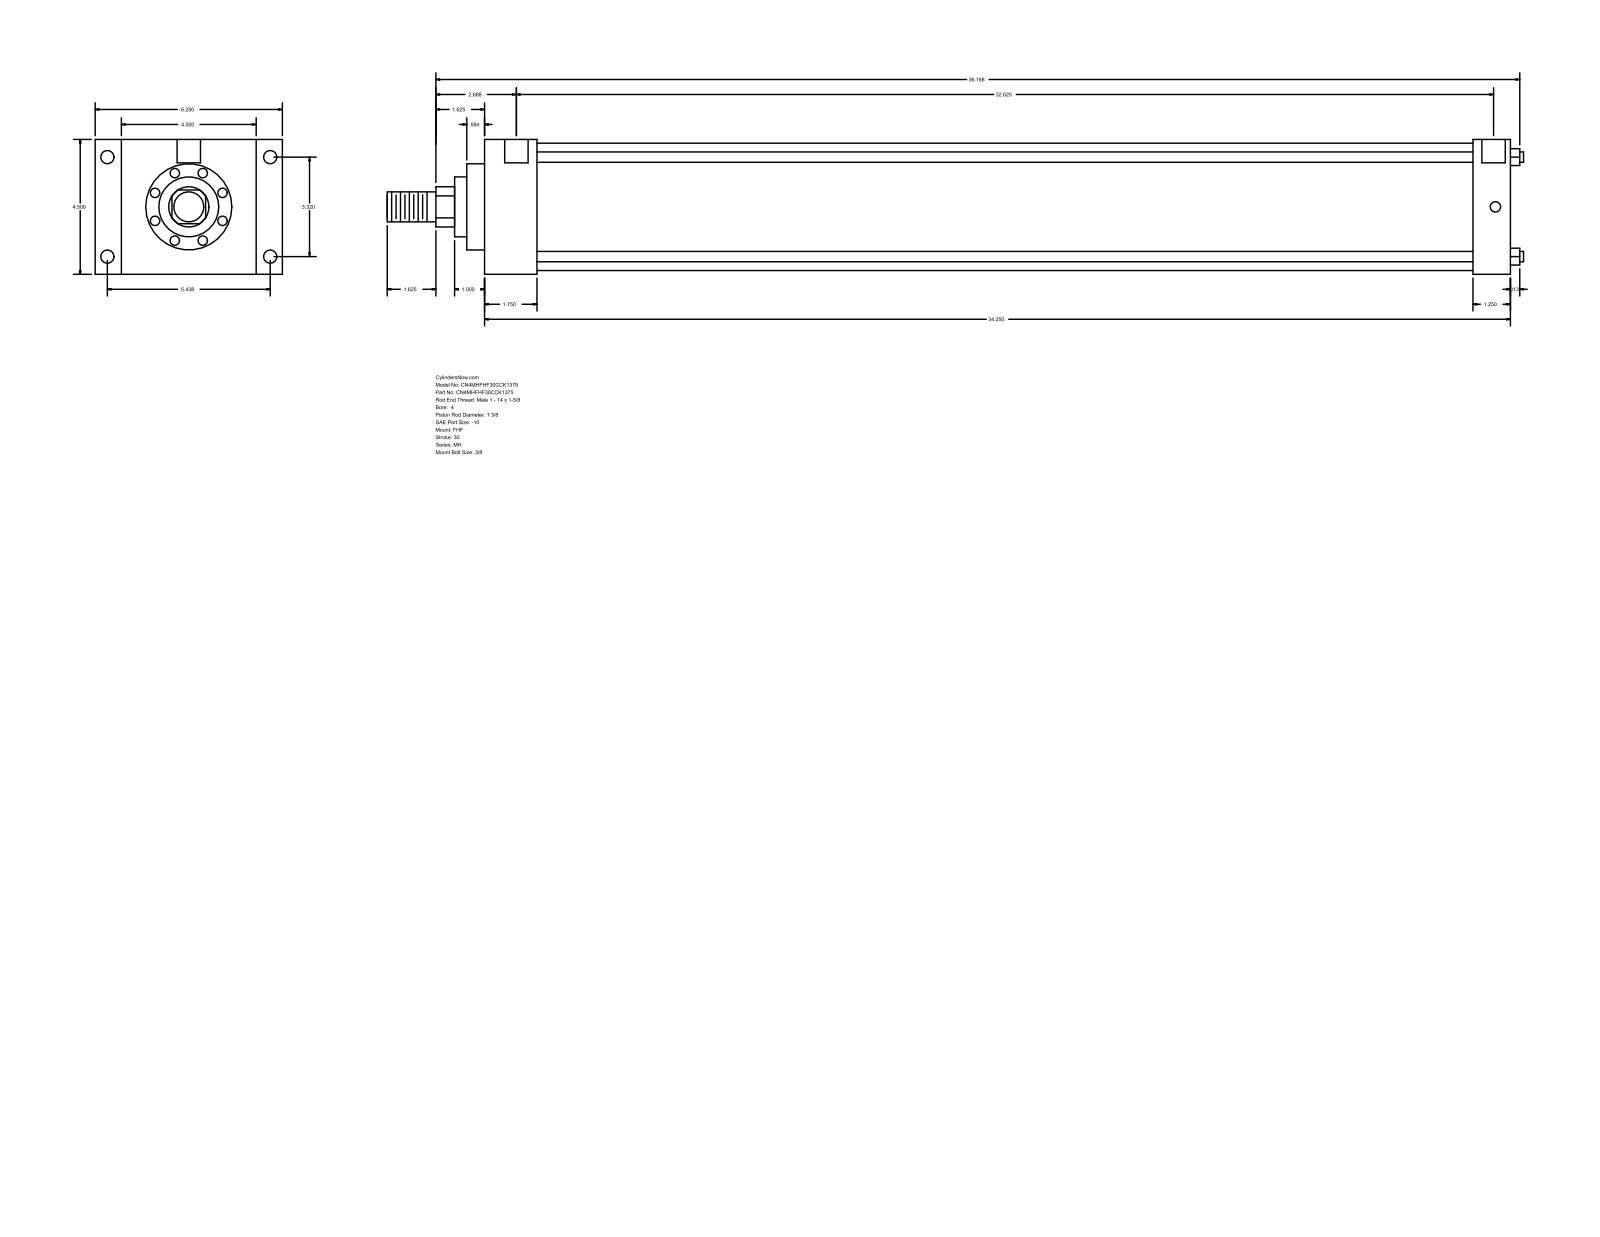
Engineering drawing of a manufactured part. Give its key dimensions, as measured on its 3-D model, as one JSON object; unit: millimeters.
{"part_name": "MH_FHF__0400_1.375", "step_written_by": "GSSL Pune (CONFIG_CONTROL_DESIGN)", "units": "millimeters", "bodies": {"solids": 0, "faces": 90, "planar": 61, "cylindrical": 29, "other": 0}, "overall_size": [963.61, 158.75, 114.3], "round_holes": [[8.73, 4], [11.13, 4], [19.84, 2]], "round_bosses_or_shafts": [[8.76, 4], [107.95, 1], [73.03, 1], [50.8, 1], [34.92, 1], [25.4, 1]], "partial_cylinders_radius": [[17.06, 1]], "face_to_face_distances": [114.3, 869.96, 44.45, 825.51, 22.23, 136.53, 158.76, 838.21, 793.76, 31.75], "hole_center_spacings": [84.32, 138.12, 161.82, 831.85, 1.58, 1.59, 828.68, 830.26]}
